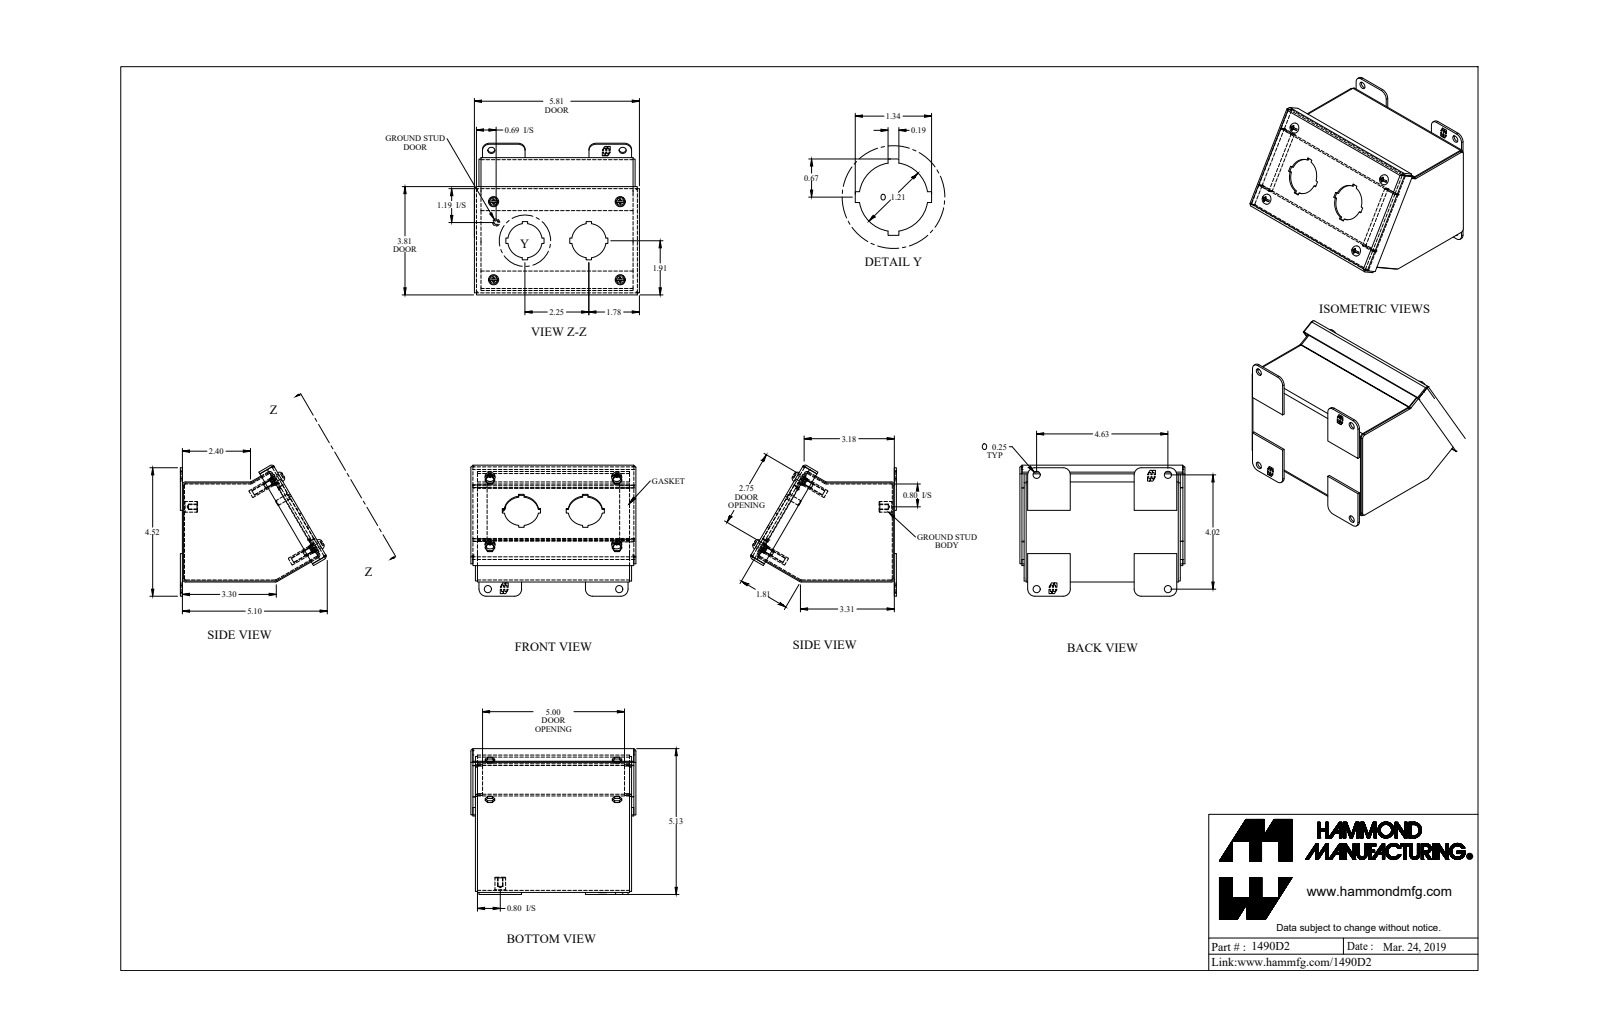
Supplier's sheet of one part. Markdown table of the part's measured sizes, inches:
| quantity | value |
| --- | --- |
| part name | 1490D2_Default |
| STEP written by | SolidWorks 2019 (CONFIG_CONTROL_DESIGN) |
| units | inches |
| bodies | 26 solids, 665 faces (469 planar, 156 cylindrical, 40 other) |
| overall size | 5.812 × 5.133 × 4.613 |
| volume | 11.98 in³ |
| surface area | 317.4 in² |
| round holes (diameter × count) | 0.25 × 8, 0.159 × 4, 1.21 × 2, 0.156 × 1 |
| round bosses / shafts (diameter × count) | 0.39 × 4, 0.275 × 4, 0.19 × 4, 0.148 × 4, 0.375 × 1, 0.25 × 1, 0.188 × 1 |
| partial cylindrical surfaces (radius × count) | 0.108 × 18, 0.036 × 12, 0.25 × 8, 0.125 × 4, 0.16 × 4, 0.171 × 4 |
| main face-to-face distances | 0.072, 5.428, 3.45, 5.356, 5.5, 3.522, 3.378, 0.144, 3.428, 0.172 |
| hole center spacings | 1.764, 3.626, 4.46, 4.474, 2.746, 2.75, 2.751, 2.755 |
